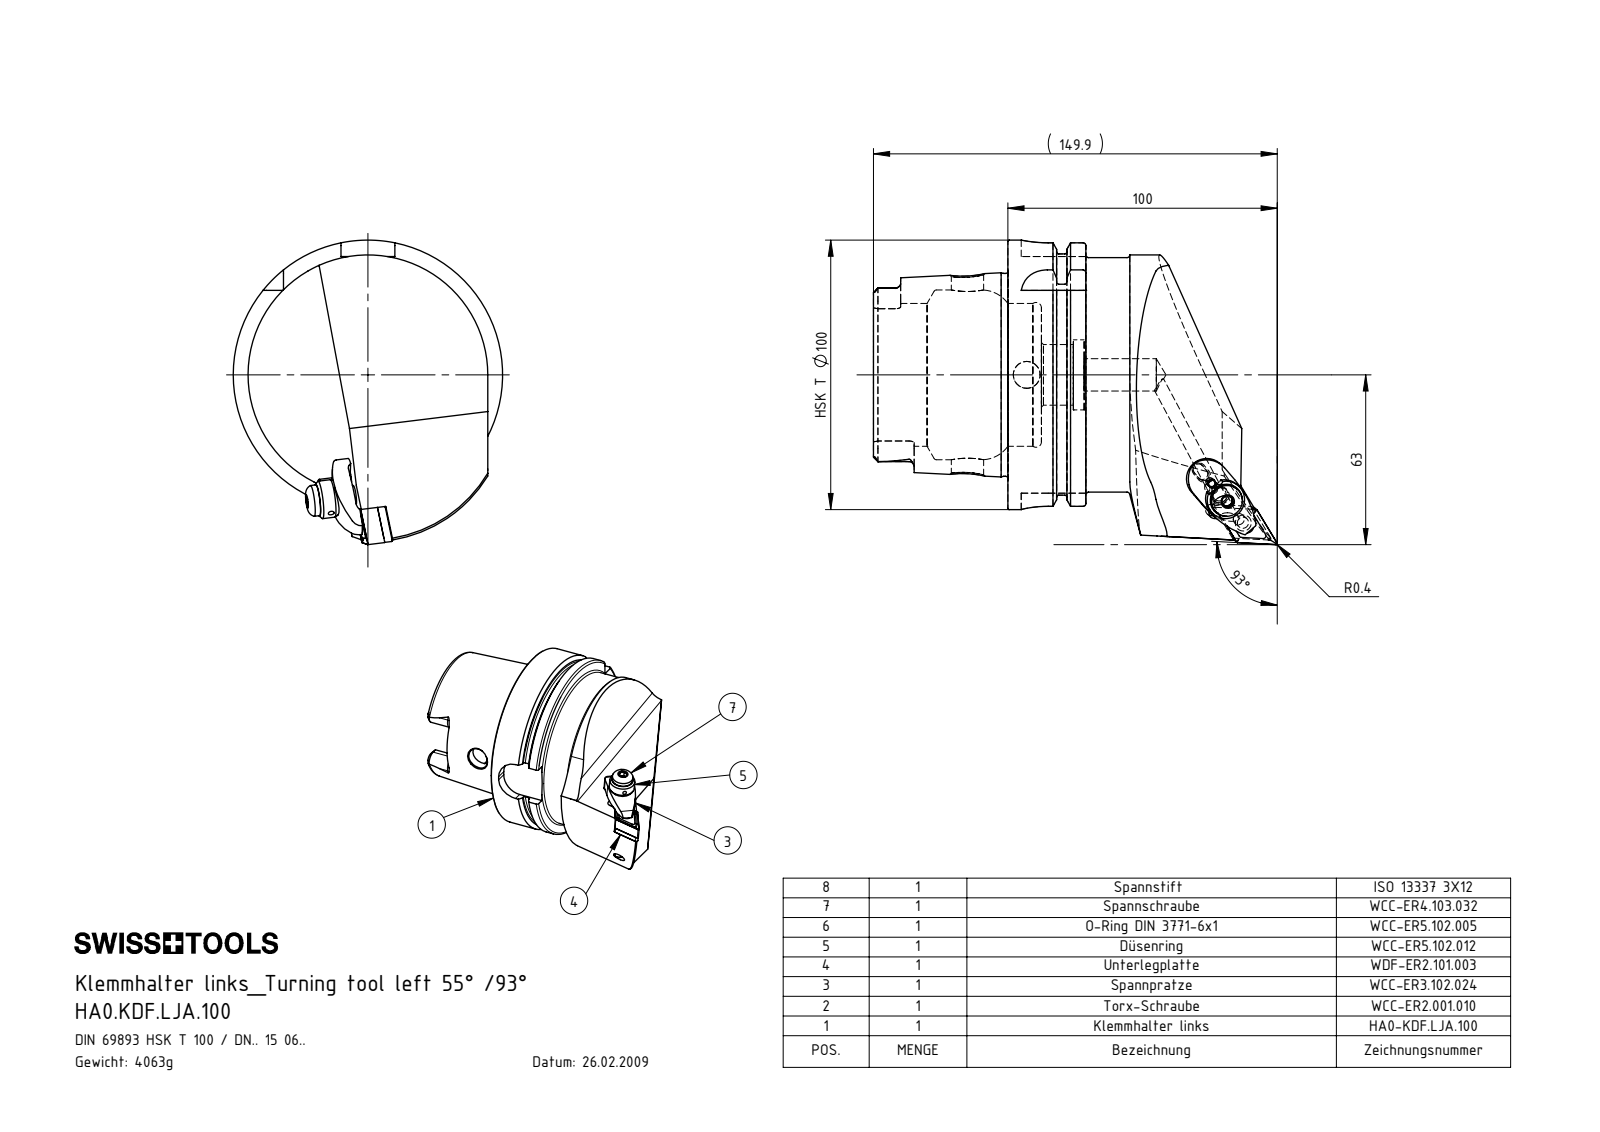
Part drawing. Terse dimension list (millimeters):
name: WCC-ER4.103.032_A; WCC-ER5.102.012_B; WCC-ER2.001.010_A; HA0-KDF.LJA.100_B_Fertigbearbeitung (+7 more)
written by: SolidWorks 2017 (AUTOMOTIVE_DESIGN)
unit: mm
bodies: 11 solids, 343 faces (121 planar, 104 cylindrical, 118 other)
size: 149.9 × 113 × 100
volume: 518 450 mm³; area: 72 672 mm²
holes: 3× ⌀2, 3× ⌀5, 2× ⌀7, 2× ⌀12, 1× ⌀2.4, 1× ⌀3, 1× ⌀4.2, 1× ⌀5.16, 1× ⌀6, 1× ⌀6.2, 1× ⌀6.4, 1× ⌀8.5
bosses: 2× ⌀6, 1× ⌀100, 1× ⌀91.95, 1× ⌀87, 1× ⌀75.26, 1× ⌀14, 1× ⌀11.5, 1× ⌀7
rounds: 6× R0.39, 6× R1.9, 4× R0.4, 4× R1, 4× R10, 3× R0.69, 3× R0.69, 3× R1.5
face distances: 12.45, 16.5, 28.95, 49.9, 62.35, 78.85, 87.8, 78.2, 28.3, 15.85
hole spacings: 7.99, 8, 8.2, 14.8, 15, 15.01, 23
